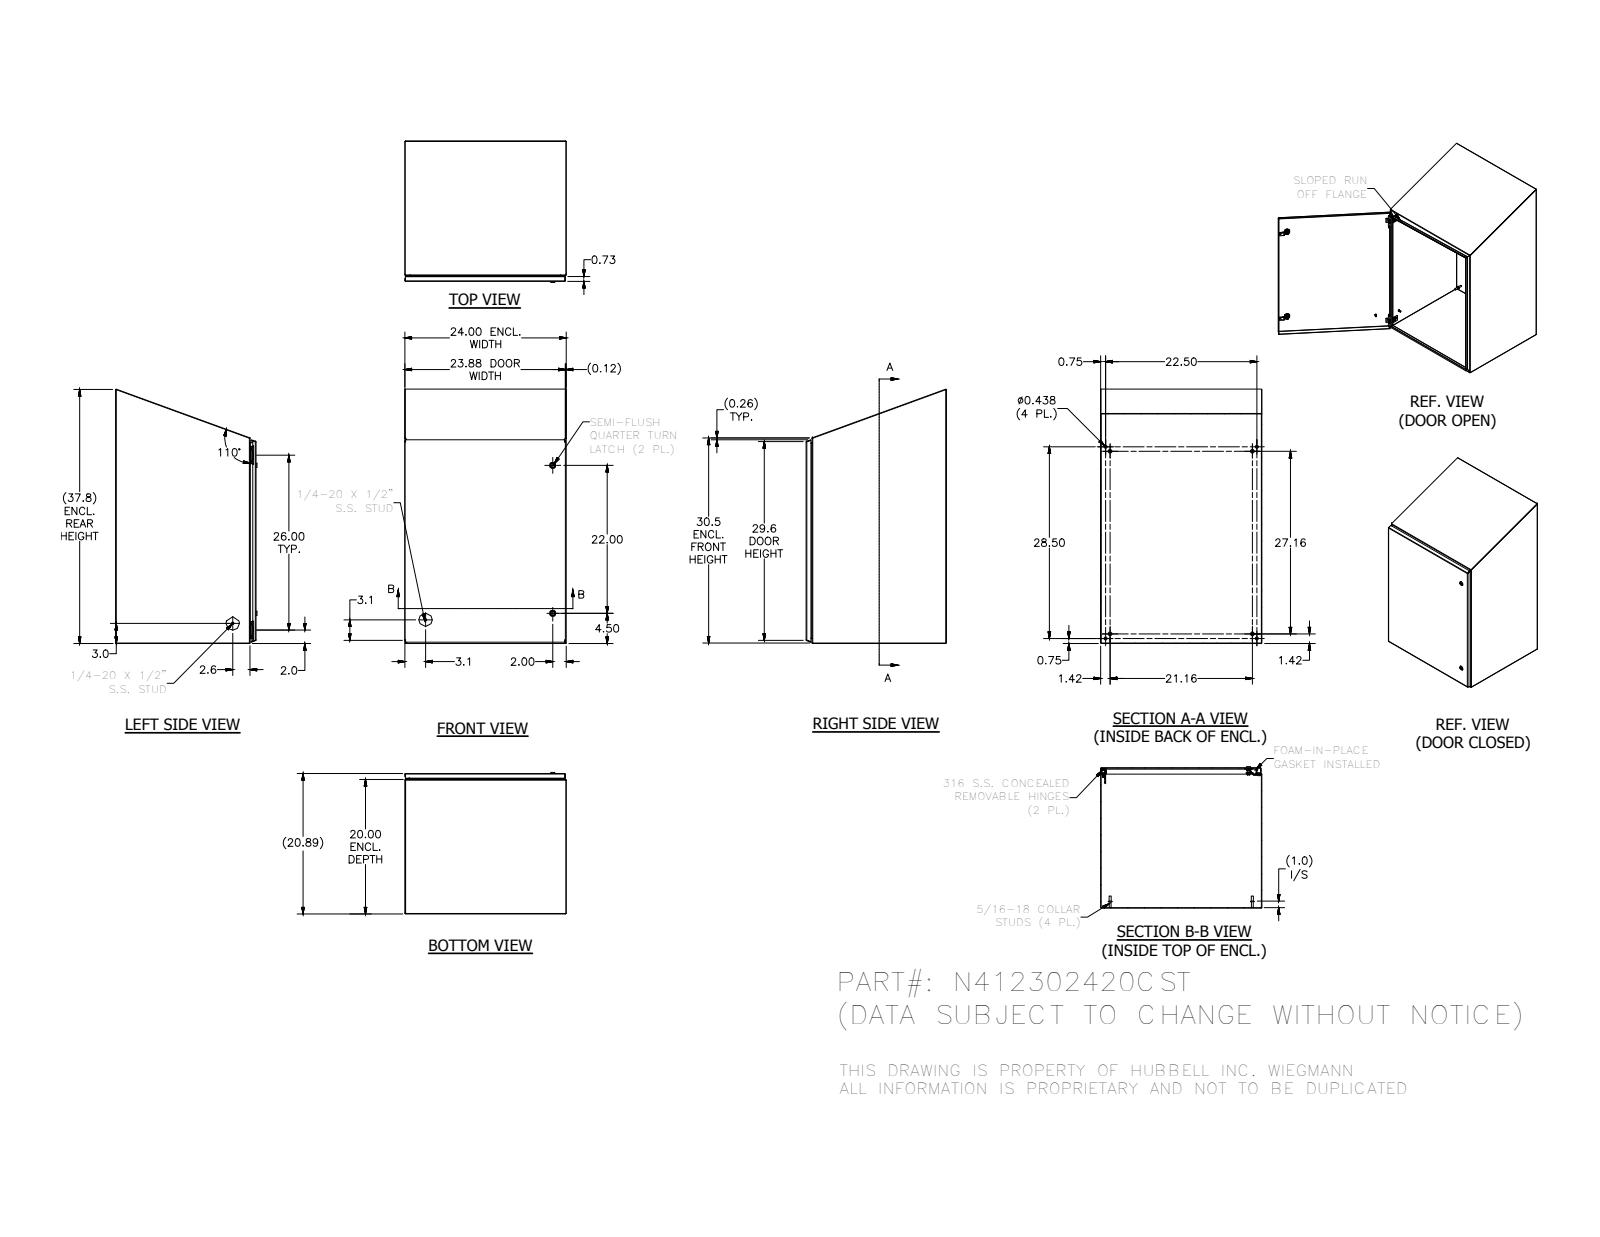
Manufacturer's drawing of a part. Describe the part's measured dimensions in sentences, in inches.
The part is named "N412_CST-assm3pcblr; N412302420CSTBLR; HFW3161; HFW328176 (+8 more)". Its 3-D file was written by "Autodesk Inventor 2012 (AUTOMOTIVE_DESIGN)". It is 41 solids with 1914 faces: 779 planar, 686 cylindrical and 449 other. Overall it measures 37.833 by 24 by 21.044 inches. Its volume is 310.8 cubic inches and its surface area 8 465 square inches. Round holes: 4 of diameter 0.093, 4 of diameter 0.152, 4 of diameter 0.167, 4 of diameter 0.172, 4 of diameter 0.187, 4 of diameter 0.437, 3 of diameter 0.156, 2 of diameter 0.197, 2 of diameter 0.315, 2 of diameter 0.394, 2 of diameter 0.402, 2 of diameter 0.634. Round bosses or shafts: 10 of diameter 0.25, 4 of diameter 0.563, 4 of diameter 0.36, 4 of diameter 0.32, 4 of diameter 0.3, 4 of diameter 0.275, 4 of diameter 0.256, 4 of diameter 0.164. Partial cylindrical surfaces (rounded edges, fillets, slot ends): 54 of radius 0.012, 28 of radius 0.031, 26 of radius 0.05, 23 of radius 0.02, 18 of radius 0.016, 18 of radius 0.105, 16 of radius 0.125, 8 of radius 0.032. The main face-to-face distances are 0.074, 20.813, 23.926, 20.887, 20.739, 23.852, 24, 19.926, 0.887, 0.813. The hole center spacings are 26, 22.869, 0.5, 0.656, 0.66, 0.984, 1.307, 1.311.
